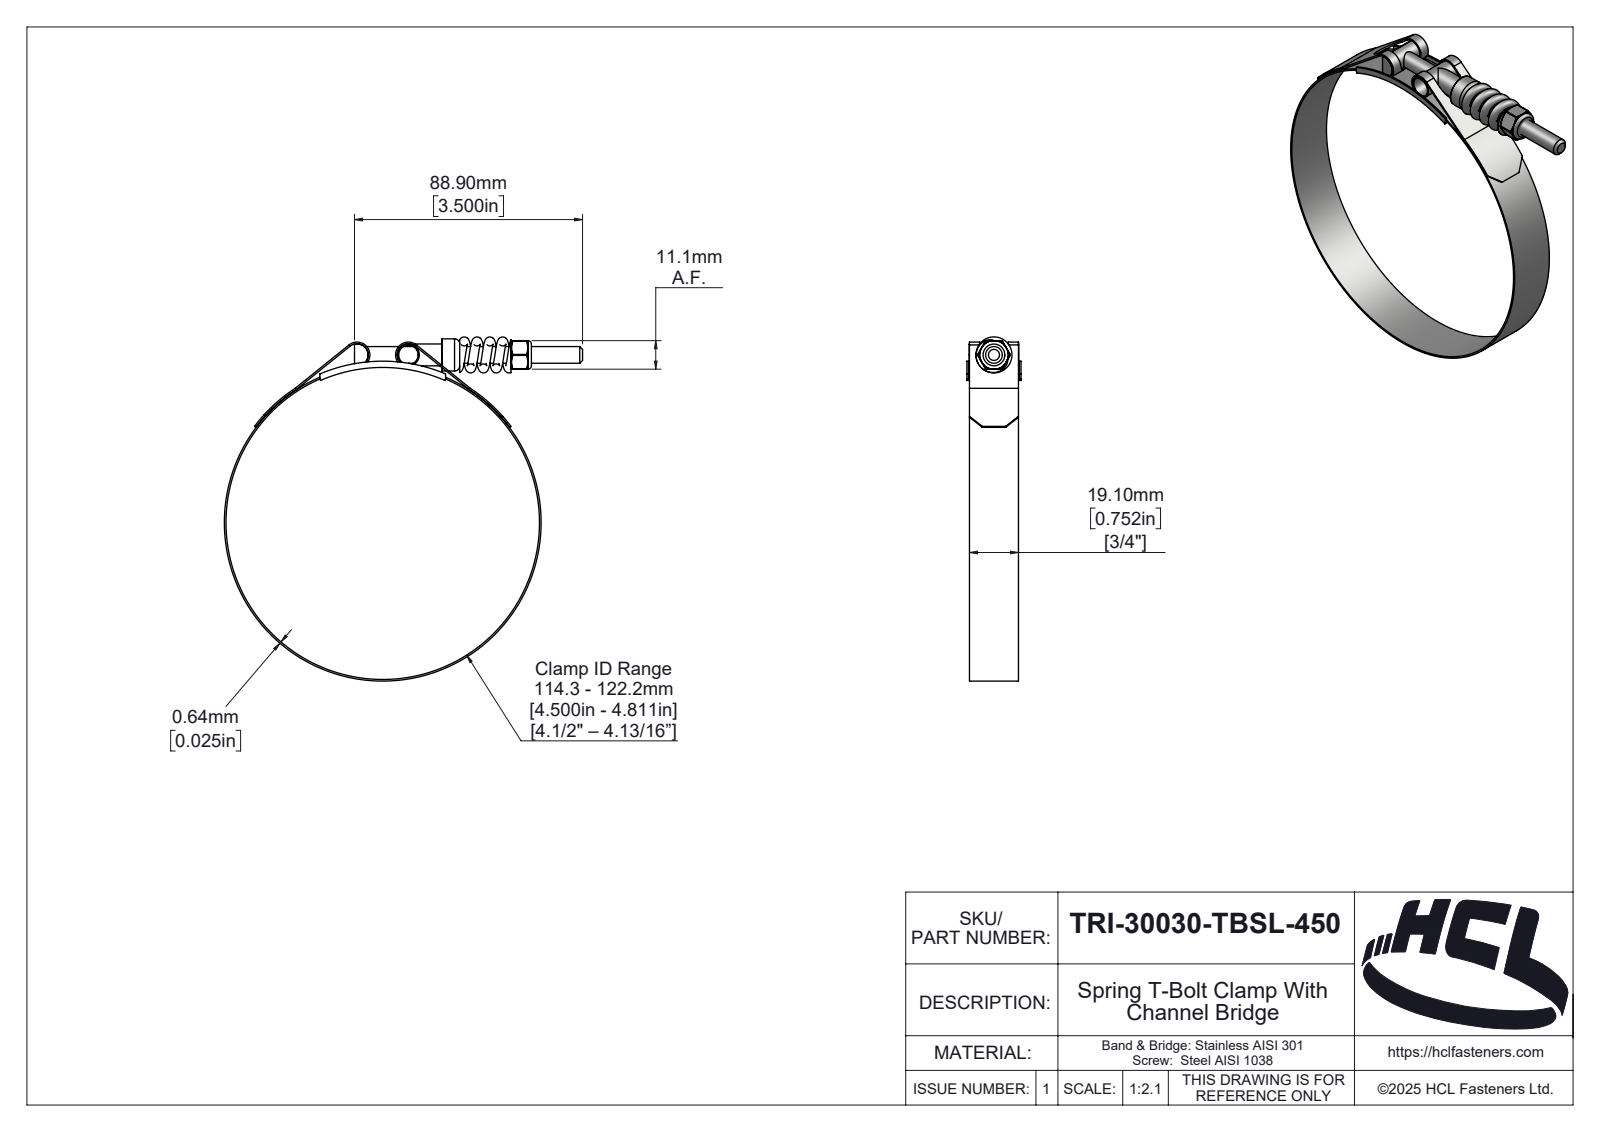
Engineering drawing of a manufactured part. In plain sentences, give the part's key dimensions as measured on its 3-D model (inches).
The part is named "TRI-30030-TBSL-450". Its 3-D file was written by "SolidWorks 2025 (AUTOMOTIVE_DESIGN)". It is 7 solids with 332 faces: 48 planar, 122 cylindrical and 162 other. Overall it measures 5.537 by 5.28 by 0.831 inches. Its volume is 0.79 cubic inches and its surface area 43.02 square inches. Round holes: 1 of diameter 0.213, 1 of diameter 0.25, 1 of diameter 0.256, 1 of diameter 0.296, 1 of diameter 4.811. Round bosses or shafts: 2 of diameter 0.335, 1 of diameter 4.861, 1 of diameter 0.493. Partial cylindrical surfaces (rounded edges, fillets, slot ends): 6 of radius 0.015, 2 of radius 0.02, 2 of radius 0.172, 2 of radius 0.197, 1 of radius 0.023, 1 of radius 0.095, 1 of radius 0.119, 1 of radius 0.126. The main face-to-face distances are 0.025, 0.752, 0.039, 0.791, 0.806, 0.014, 0.766, 0.831, 2.402, 0.438. The hole center spacings are 2.602.
